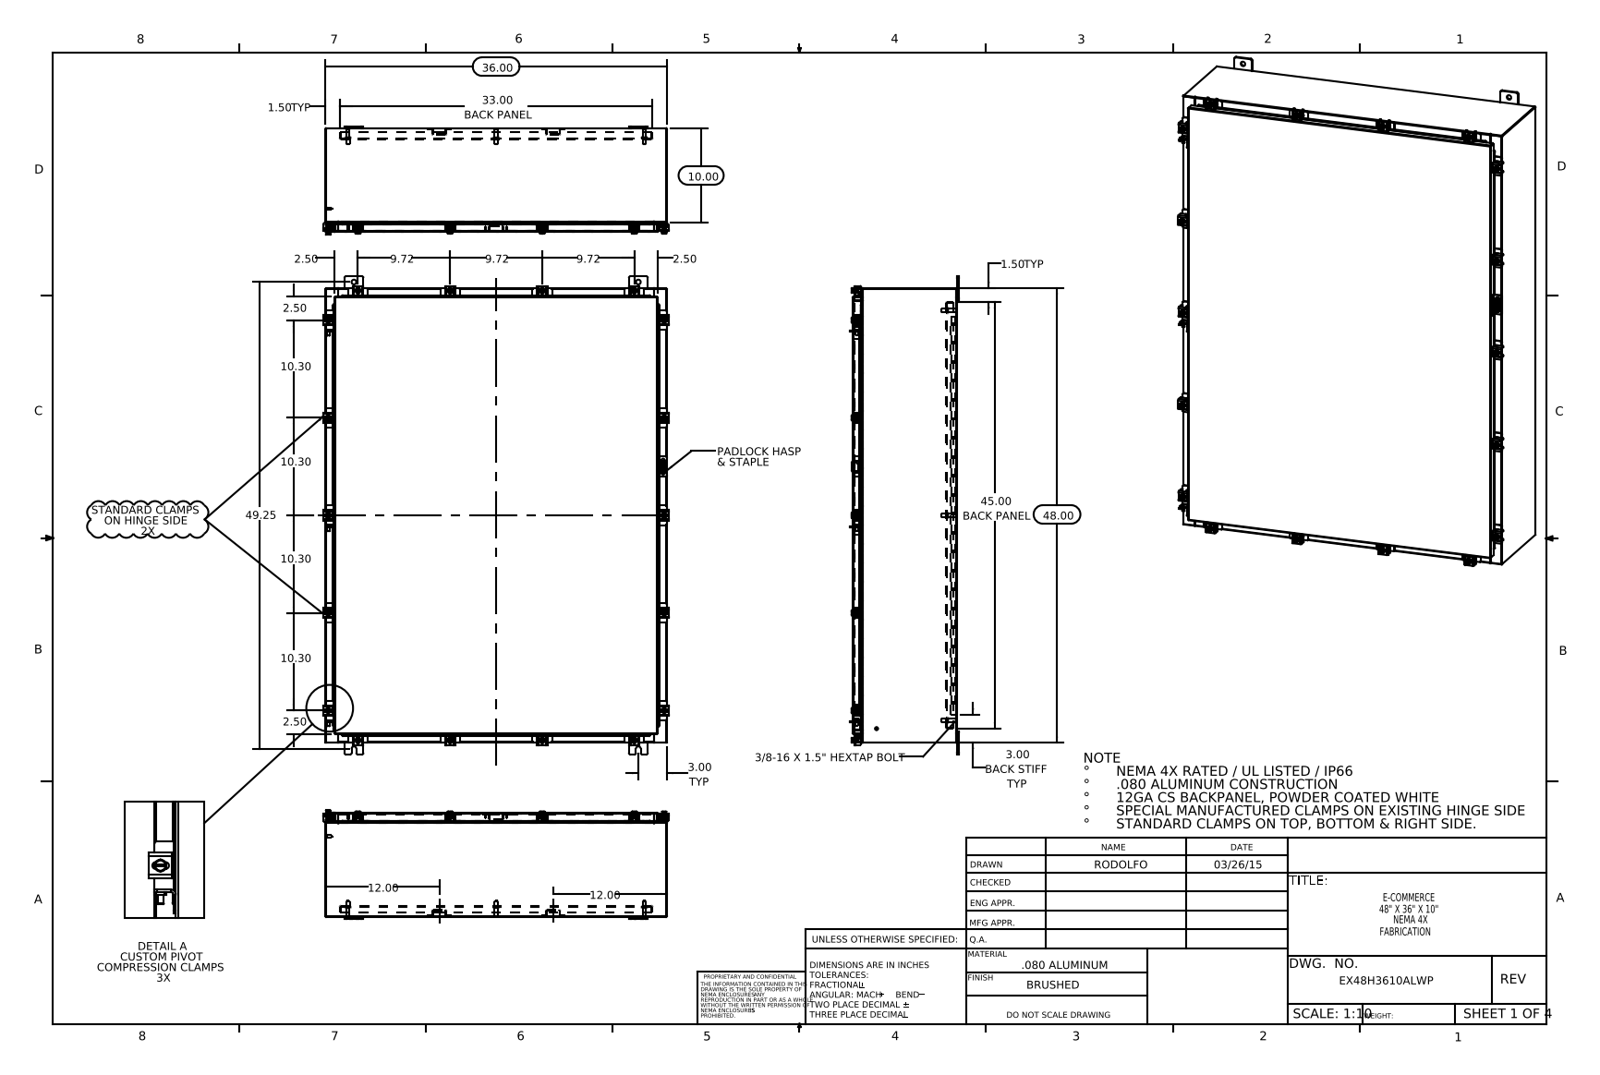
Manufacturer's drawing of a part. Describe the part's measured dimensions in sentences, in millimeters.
The part is named "EX48H3610ALWP Standard Clamps; EX48H3610ALWP Special Clamp; 22104005_DEFAULT_RTP30; EX48H3610ALWP Body (+8 more)". Its 3-D file was written by "SolidWorks 2014 (CONFIG_CONTROL_DESIGN)". It is 128 solids with 3145 faces: 1631 planar, 1216 cylindrical and 298 other. Overall it measures 1282.7 by 925.1 by 290.9 millimeters. Its volume is 10 220 000 cubic millimeters and its surface area 9 982 000 square millimeters. Round holes: 18 of diameter 5.4, 18 of diameter 6.6, 12 of diameter 12.7, 7 of diameter 6.4, 1 of diameter 3.2. Round bosses or shafts: 18 of diameter 12.7, 18 of diameter 6.4, 15 of diameter 10.1, 8 of diameter 15.9, 8 of diameter 9.5, 8 of diameter 8.4, 6 of diameter 4, 6 of diameter 3.6. Partial cylindrical surfaces (rounded edges, fillets, slot ends): 76 of radius 1.5, 38 of radius 0.3, 36 of radius 3.6, 34 of radius 2.2, 33 of radius 3, 27 of radius 1.3, 27 of radius 2.3, 26 of radius 3.7. The main face-to-face distances are 1.9, 276.9, 275, 278.8, 2.6, 25.4, 27.3, 249.6, 251.5, 29.9. The hole center spacings are 50, 59.6, 112.8, 354.9, 374.1, 409.6, 422.2, 451.
